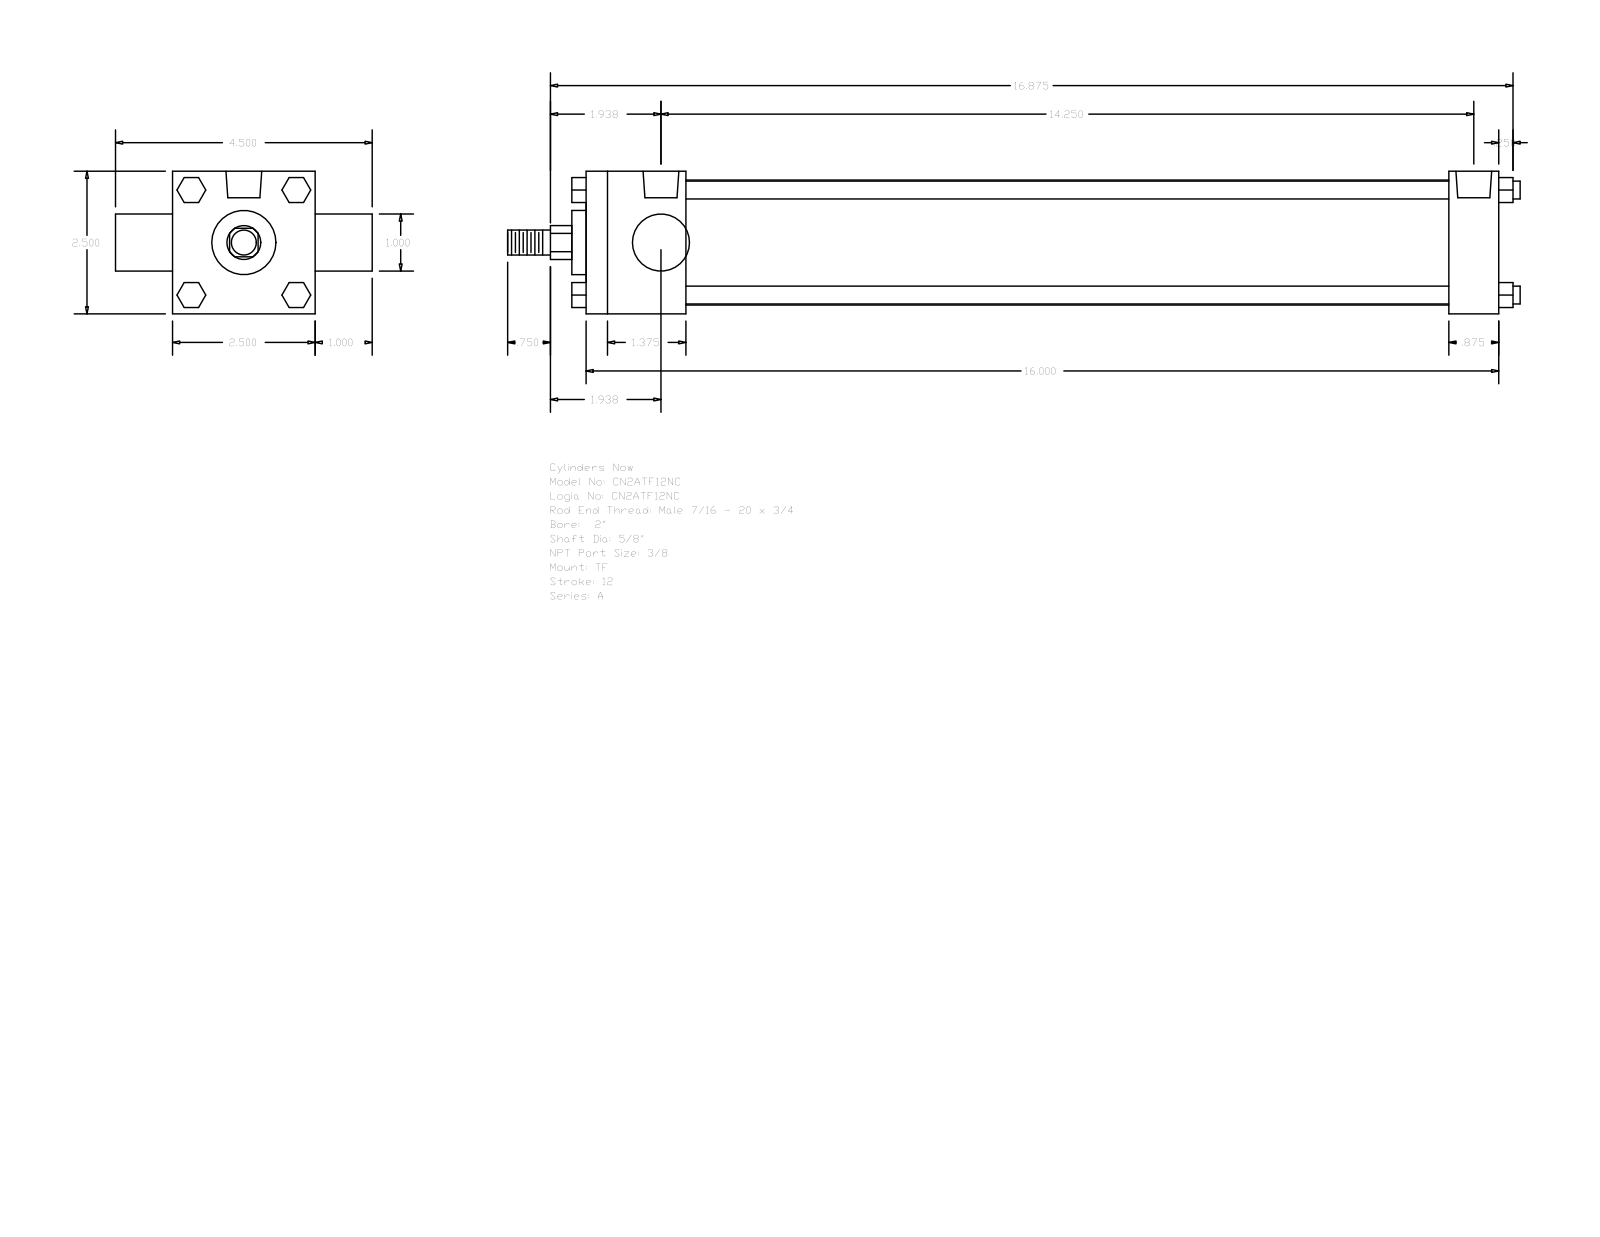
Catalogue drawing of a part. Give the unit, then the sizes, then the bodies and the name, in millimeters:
Units: millimetres
Overall size (bounding box): 450.85 × 114.3 × 63.5
Round holes (diameter × count): ⌀5.56 ×3, ⌀15.93 ×2
Round bosses / shafts (diameter × count): ⌀7.94 ×4, ⌀55.63 ×1, ⌀28.57 ×1, ⌀25.4 ×1, ⌀15.88 ×1, ⌀11.11 ×1
Partial cylindrical surfaces — rounded edges, fillets, slot ends (radius × count): R7.54 ×1
Main face-to-face distances: 63.5, 406.39, 44.45, 384.17, 339.72, 361.94, 22.22, 25.4, 88.9, 6.35
Hole centre spacings: 3.97, 3.98, 354, 357.97, 357.98, 361.95
Bodies: 0 solids, 120 faces (92 planar, 28 cylindrical, 0 other)
Part name (STEP PRODUCT): A_TF__0200_0.625
STEP written by: GSSL Pune (CONFIG_CONTROL_DESIGN)
